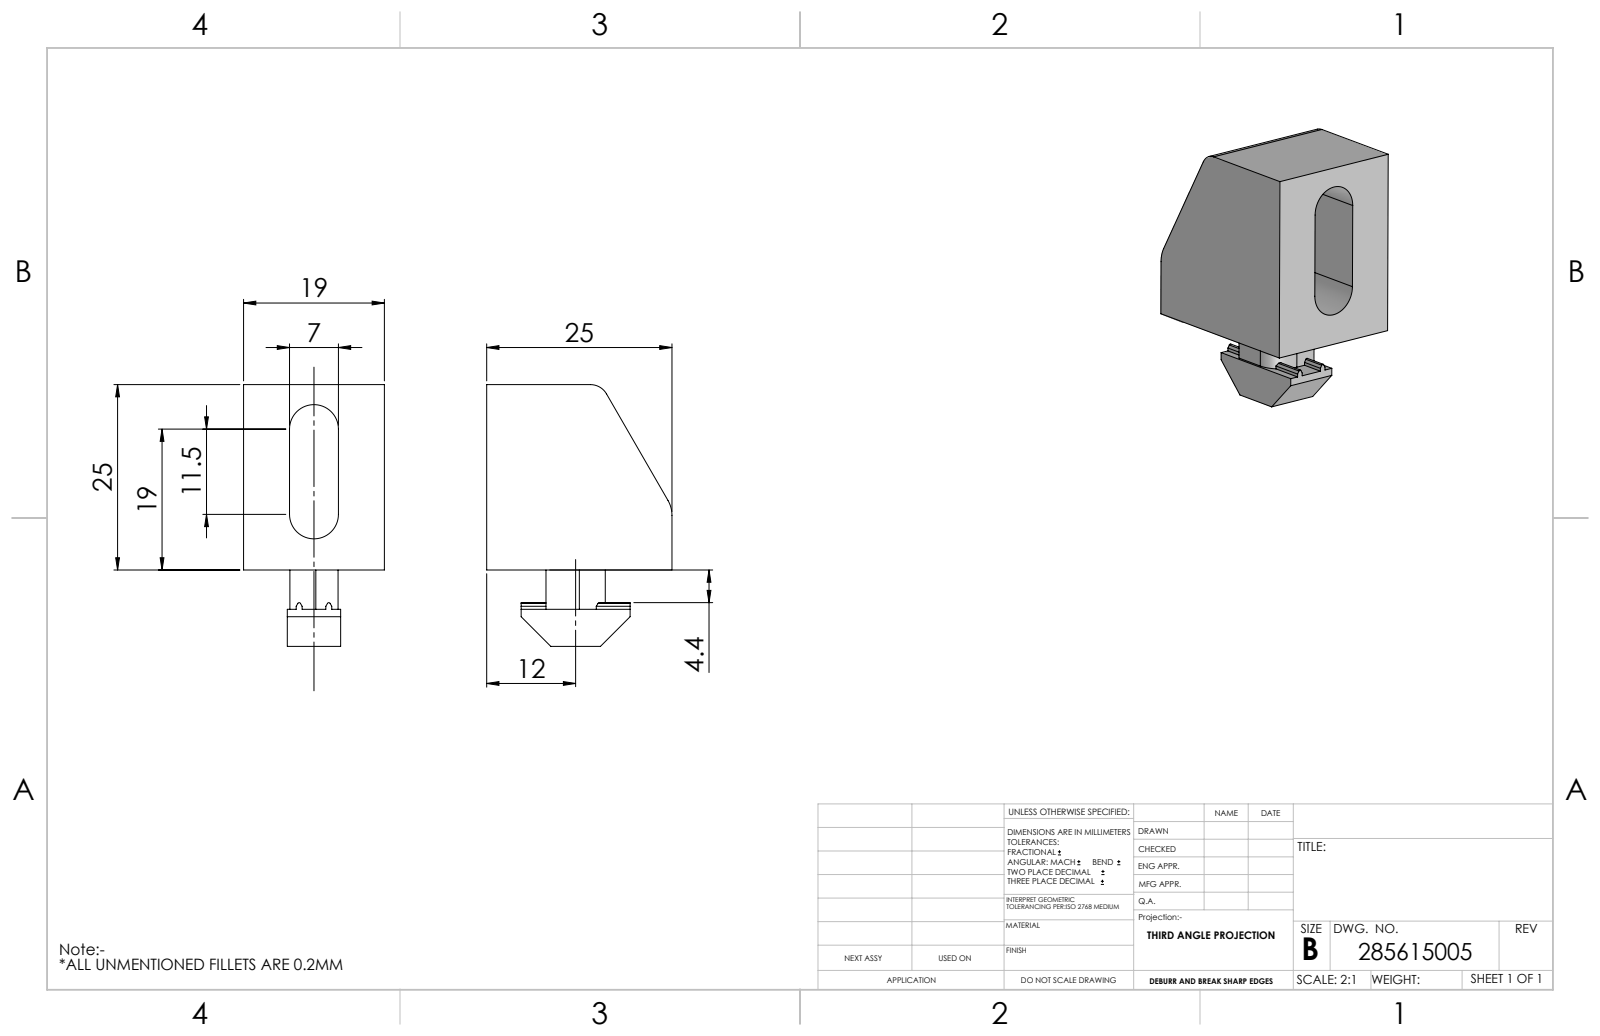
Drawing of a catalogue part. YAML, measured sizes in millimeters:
part_name: "285615005"
step_written_by: "SolidWorks 2014 (AUTOMOTIVE_DESIGN)"
units: millimeters
bodies: {solids: 1, faces: 51, planar: 40, cylindrical: 11, other: 0}
overall_size: [35.3, 25, 19]
volume: 8612
surface_area: 4001
partial_cylinders:
  - {radius: 0.2, count: 2}
  - {radius: 3.3, count: 2}
  - {radius: 3.5, count: 2}
  - {radius: 2.5, count: 1}
  - {radius: 4, count: 1}
face_to_face_distances: [19, 6.2, 12.8, 25, 6.6, 5.9, 13.1, 6.9, 7.2, 10.3]
